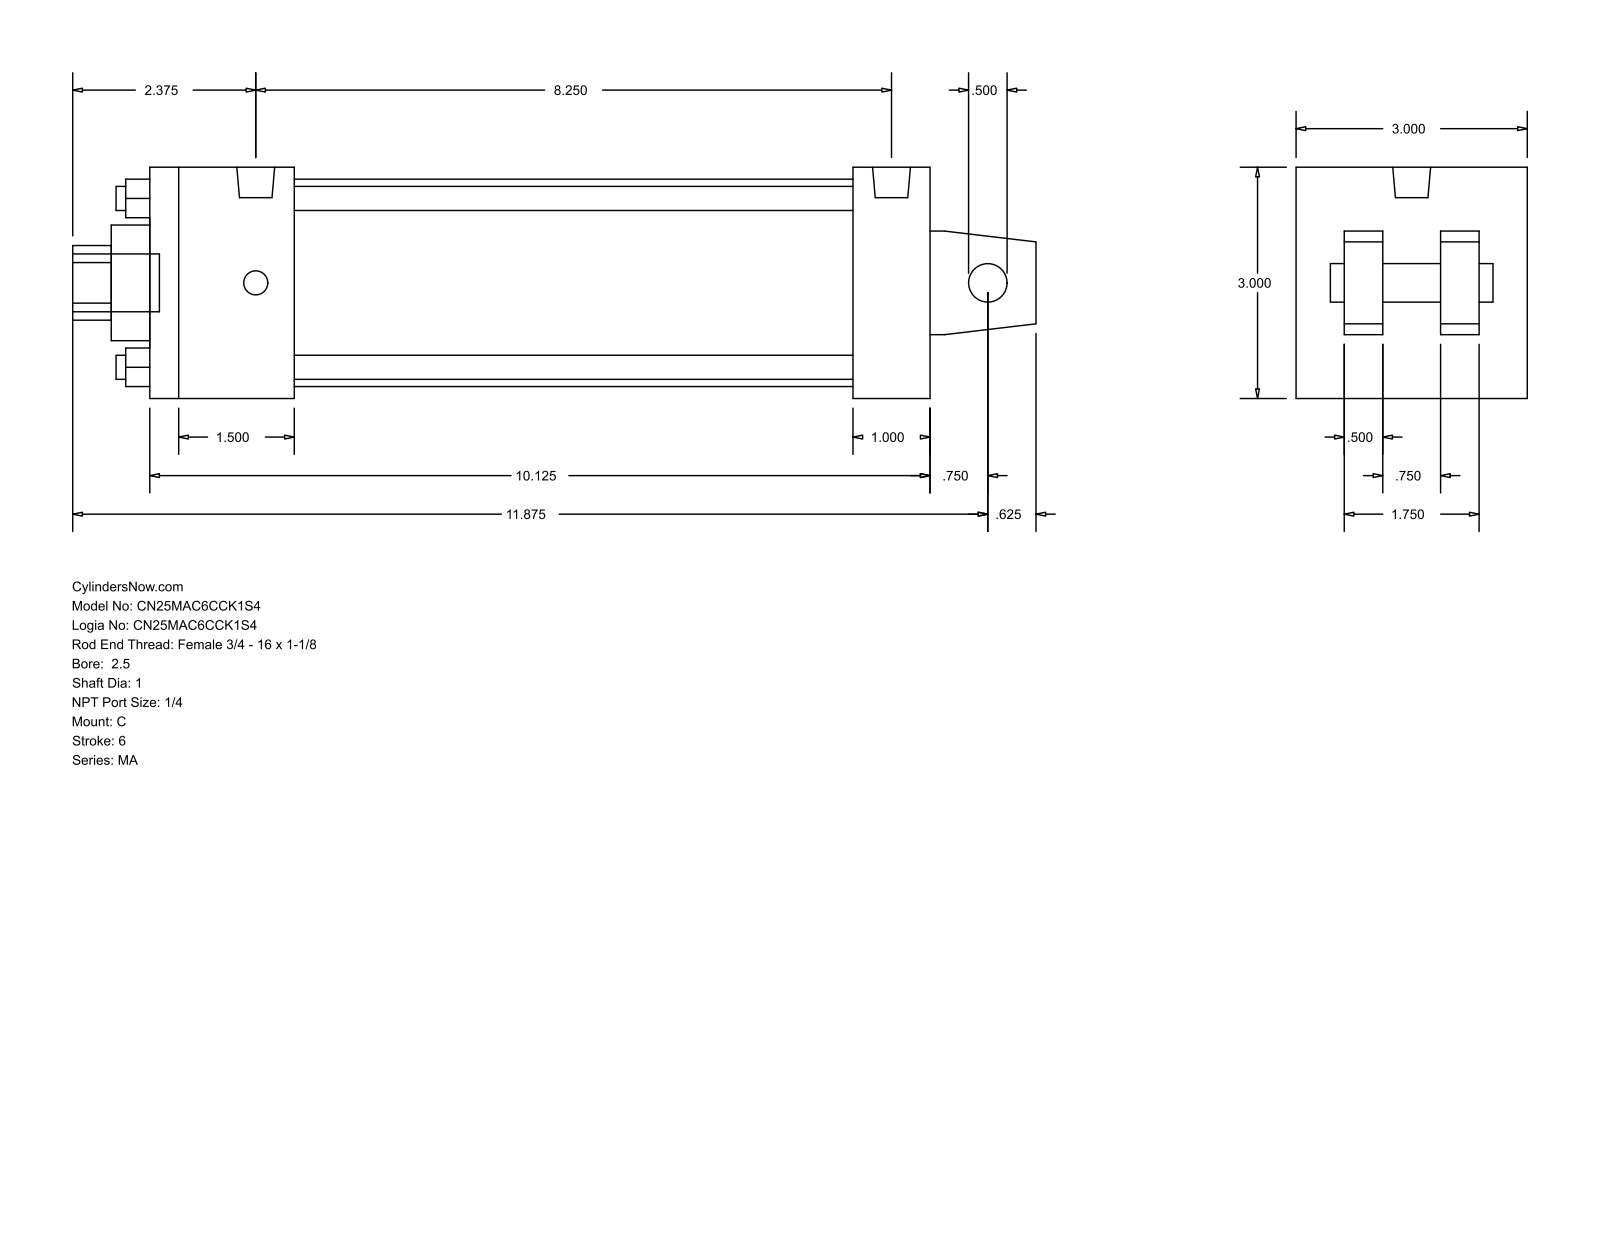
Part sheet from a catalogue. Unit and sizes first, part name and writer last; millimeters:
Units: millimetres
Overall size (bounding box): 317.5 × 76.2 × 76.2
Round holes (diameter × count): ⌀7.94 ×4, ⌀12.7 ×1, ⌀25.4 ×1, ⌀38.1 ×1, ⌀68.33 ×1
Round bosses / shafts (diameter × count): ⌀7.94 ×4, ⌀12.49 ×2, ⌀19.05 ×1
Partial cylindrical surfaces — rounded edges, fillets, slot ends (radius × count): R12.29 ×1
Main face-to-face distances: 76.2, 47.63, 257.17, 12.7, 15.87, 60.33, 28.57, 231.78, 184.15, 209.54
Hole centre spacings: 39.33, 55.62, 78.66
Bodies: 0 solids, 103 faces (76 planar, 27 cylindrical, 0 other)
Part name (STEP PRODUCT): MA_C__0250_1
STEP written by: GSSL Pune (CONFIG_CONTROL_DESIGN)
